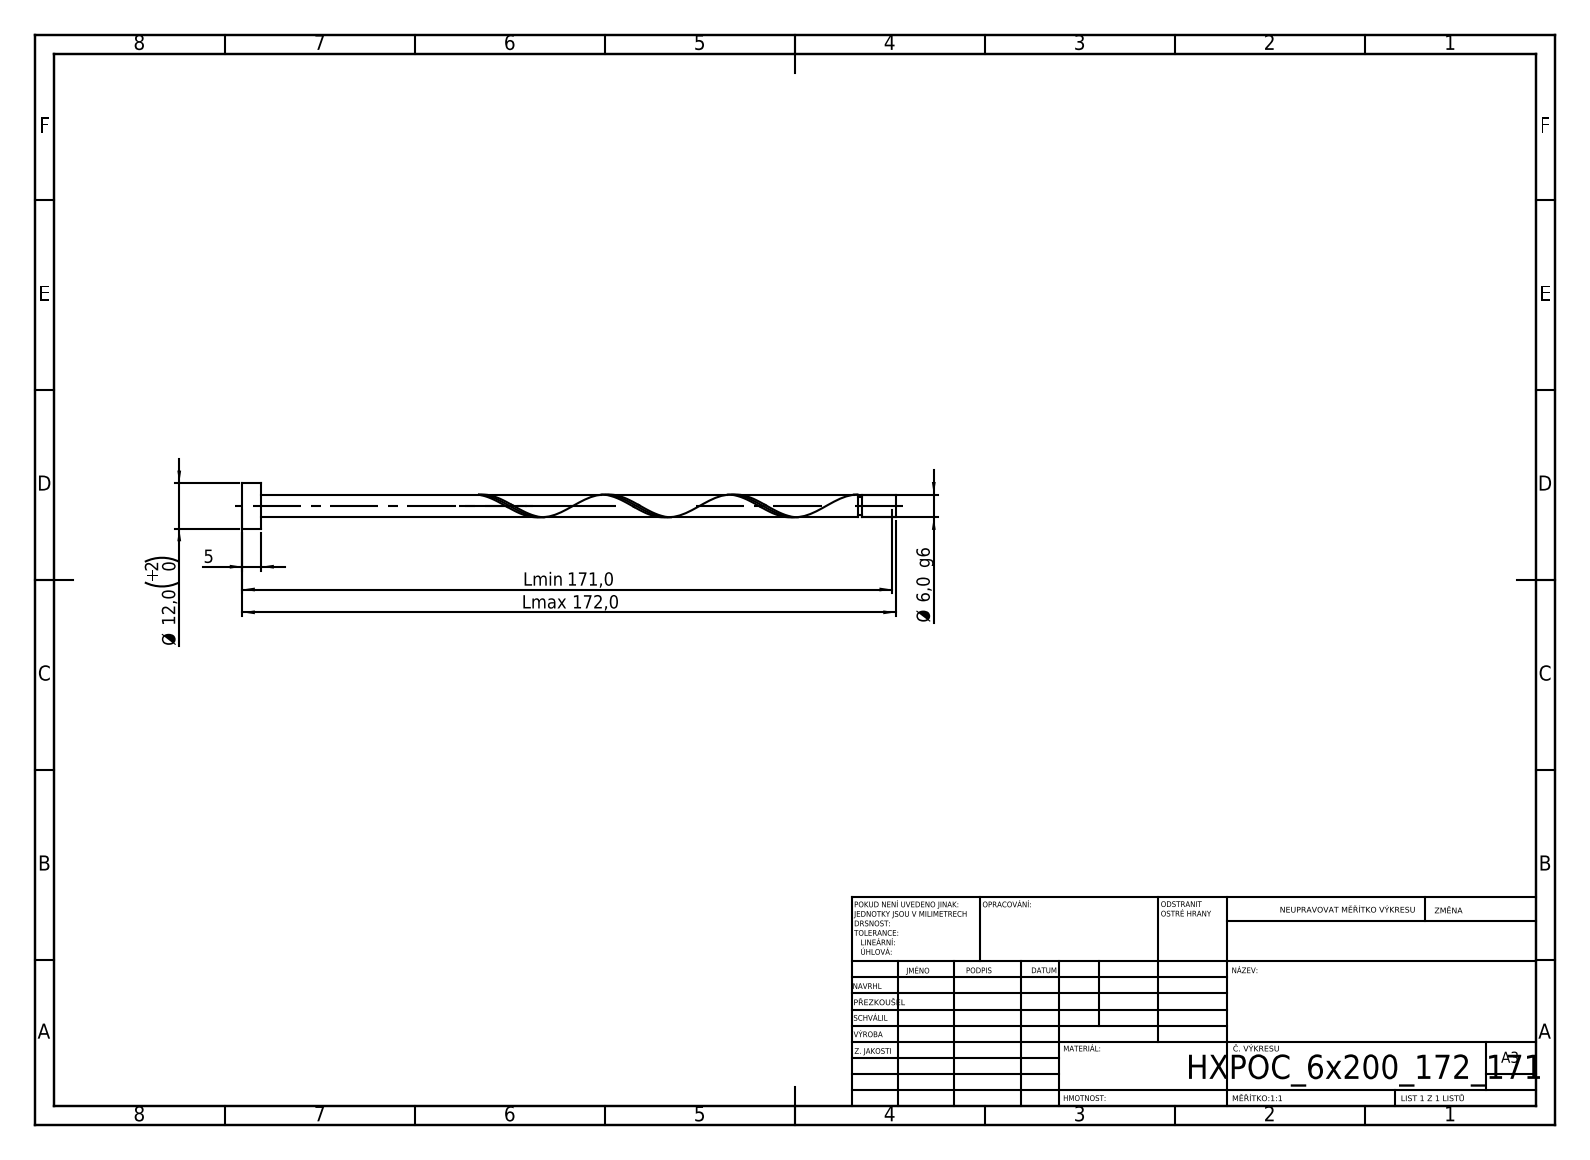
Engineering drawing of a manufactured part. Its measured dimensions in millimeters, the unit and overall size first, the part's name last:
Units: millimetres
Overall size (bounding box): 172 × 12 × 12
Round bosses / shafts (diameter × count): ⌀12 ×1, ⌀6 ×1, ⌀4.8 ×1
Main face-to-face distances: 5, 172, 167, 163.23, 158.23, 8.77, 162.03, 157.03, 1.2, 9.97
Volume: 5 221 mm³ · Surface area: 3 647 mm²
Bodies: 1 solid, 21 faces (6 planar, 14 cylindrical, 1 other)
STEP written by: SolidWorks 2019 (CONFIG_CONTROL_DESIGN)
